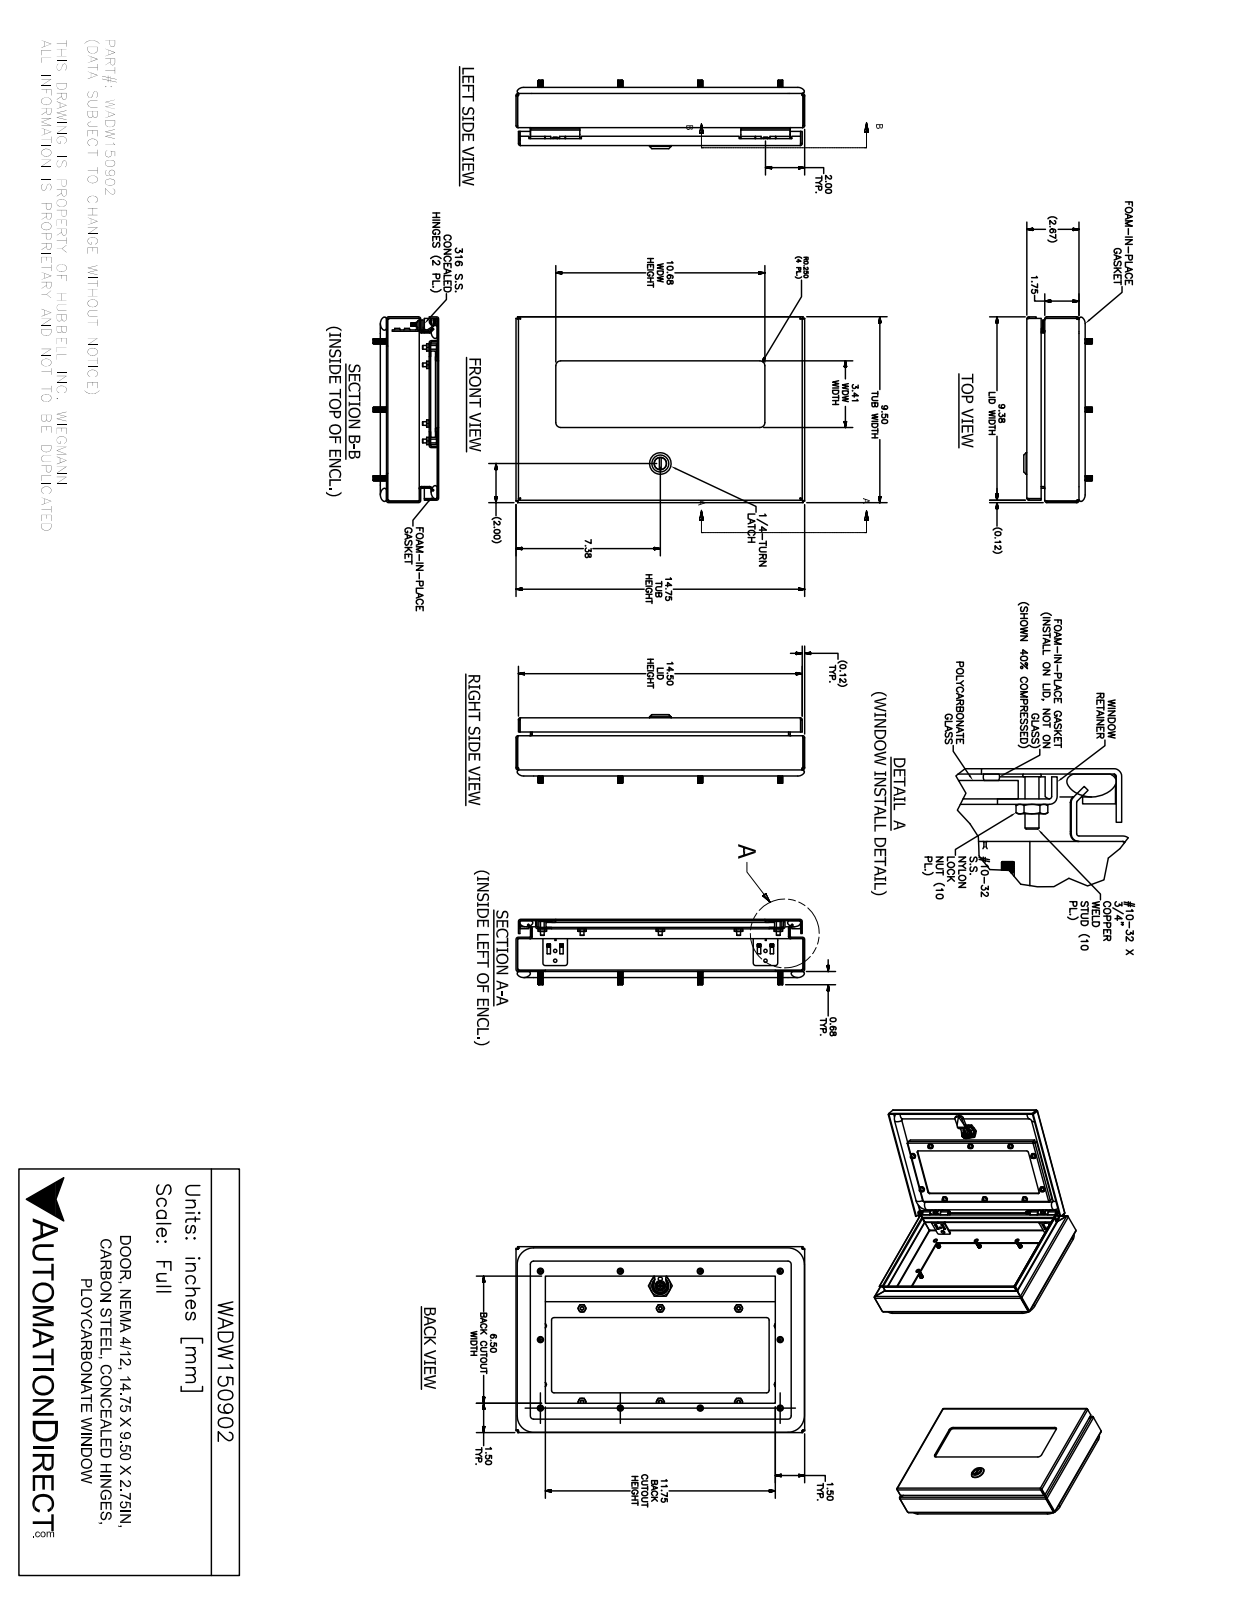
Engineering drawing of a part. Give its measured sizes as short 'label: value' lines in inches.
name: WADW150902
written by: SolidWorks 2017 (AUTOMOTIVE_DESIGN)
unit: in
bodies: 63 solids, 2144 faces (739 planar, 778 cylindrical, 627 other)
size: 14.75 × 9.5 × 3.501
volume: 58.1 in³; area: 1 104 in²
holes: 12× ⌀0.156, 10× ⌀0.249, 10× ⌀0.281, 4× ⌀0.093, 4× ⌀0.152, 4× ⌀0.167, 4× ⌀0.172, 4× ⌀0.188, 1× ⌀0.187, 1× ⌀0.197, 1× ⌀0.315, 1× ⌀0.394
bosses: 28× ⌀0.25, 10× ⌀0.32, 10× ⌀0.313, 10× ⌀0.19, 10× ⌀0.188, 4× ⌀0.36, 4× ⌀0.32, 4× ⌀0.256
rounds: 34× R0.031, 30× R0.012, 26× R0.05, 24× R0.105, 20× R0.125, 18× R0.016, 13× R0.02, 8× R0.032
face distances: 0.074, 2.593, 0.411, 2.182, 2.667, 2.256, 0.337, 1.676, 2.519, 0.25
hole spacings: 8.104, 10.746, 3.5, 4, 4.083, 5.378, 6.237, 7
